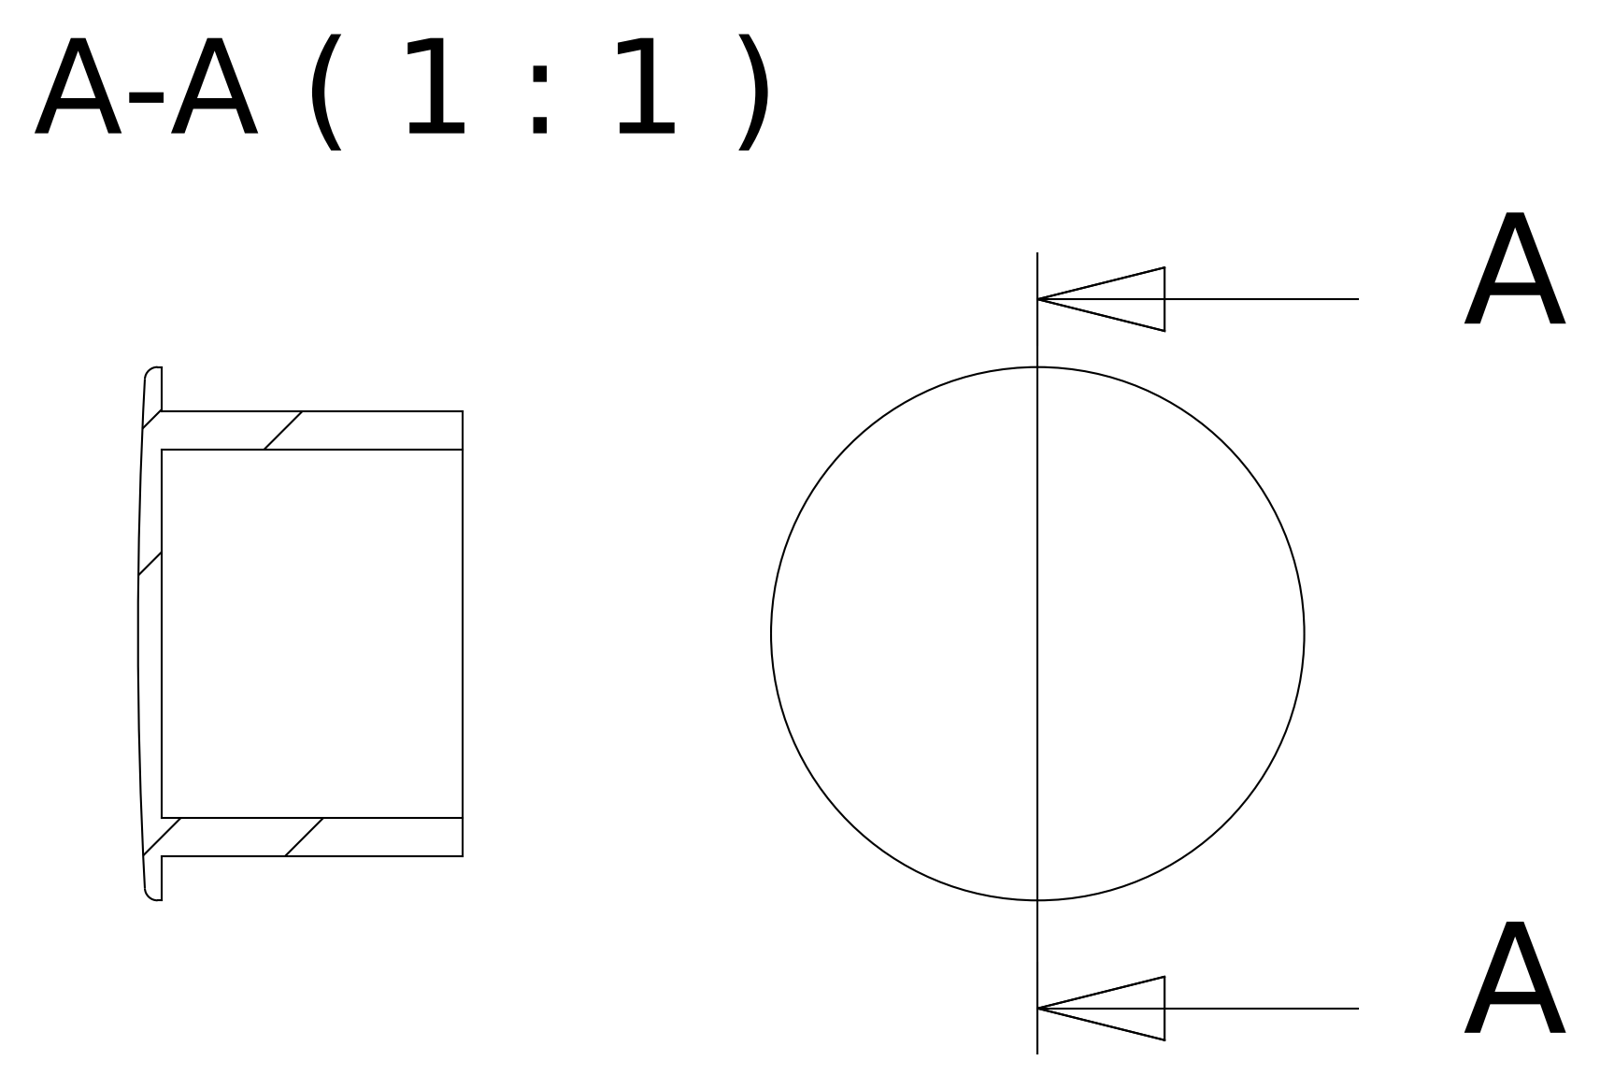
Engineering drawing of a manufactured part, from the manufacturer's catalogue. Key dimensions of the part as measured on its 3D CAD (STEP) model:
Part name (STEP PRODUCT): 18.079.00
STEP written by: Autodesk Inventor 2016 (AUTOMOTIVE_DESIGN)
Units: millimetres
Bodies: 1 solid, 8 faces (3 planar, 3 cylindrical, 2 other)
Overall size (bounding box): 16.8 × 16.8 × 10.24
Volume: 594 mm³ · Surface area: 1 226 mm²
Round holes (diameter × count): ⌀11.6 ×1
Round bosses / shafts (diameter × count): ⌀16.8 ×1, ⌀14 ×1
Main face-to-face distances: 9.5
